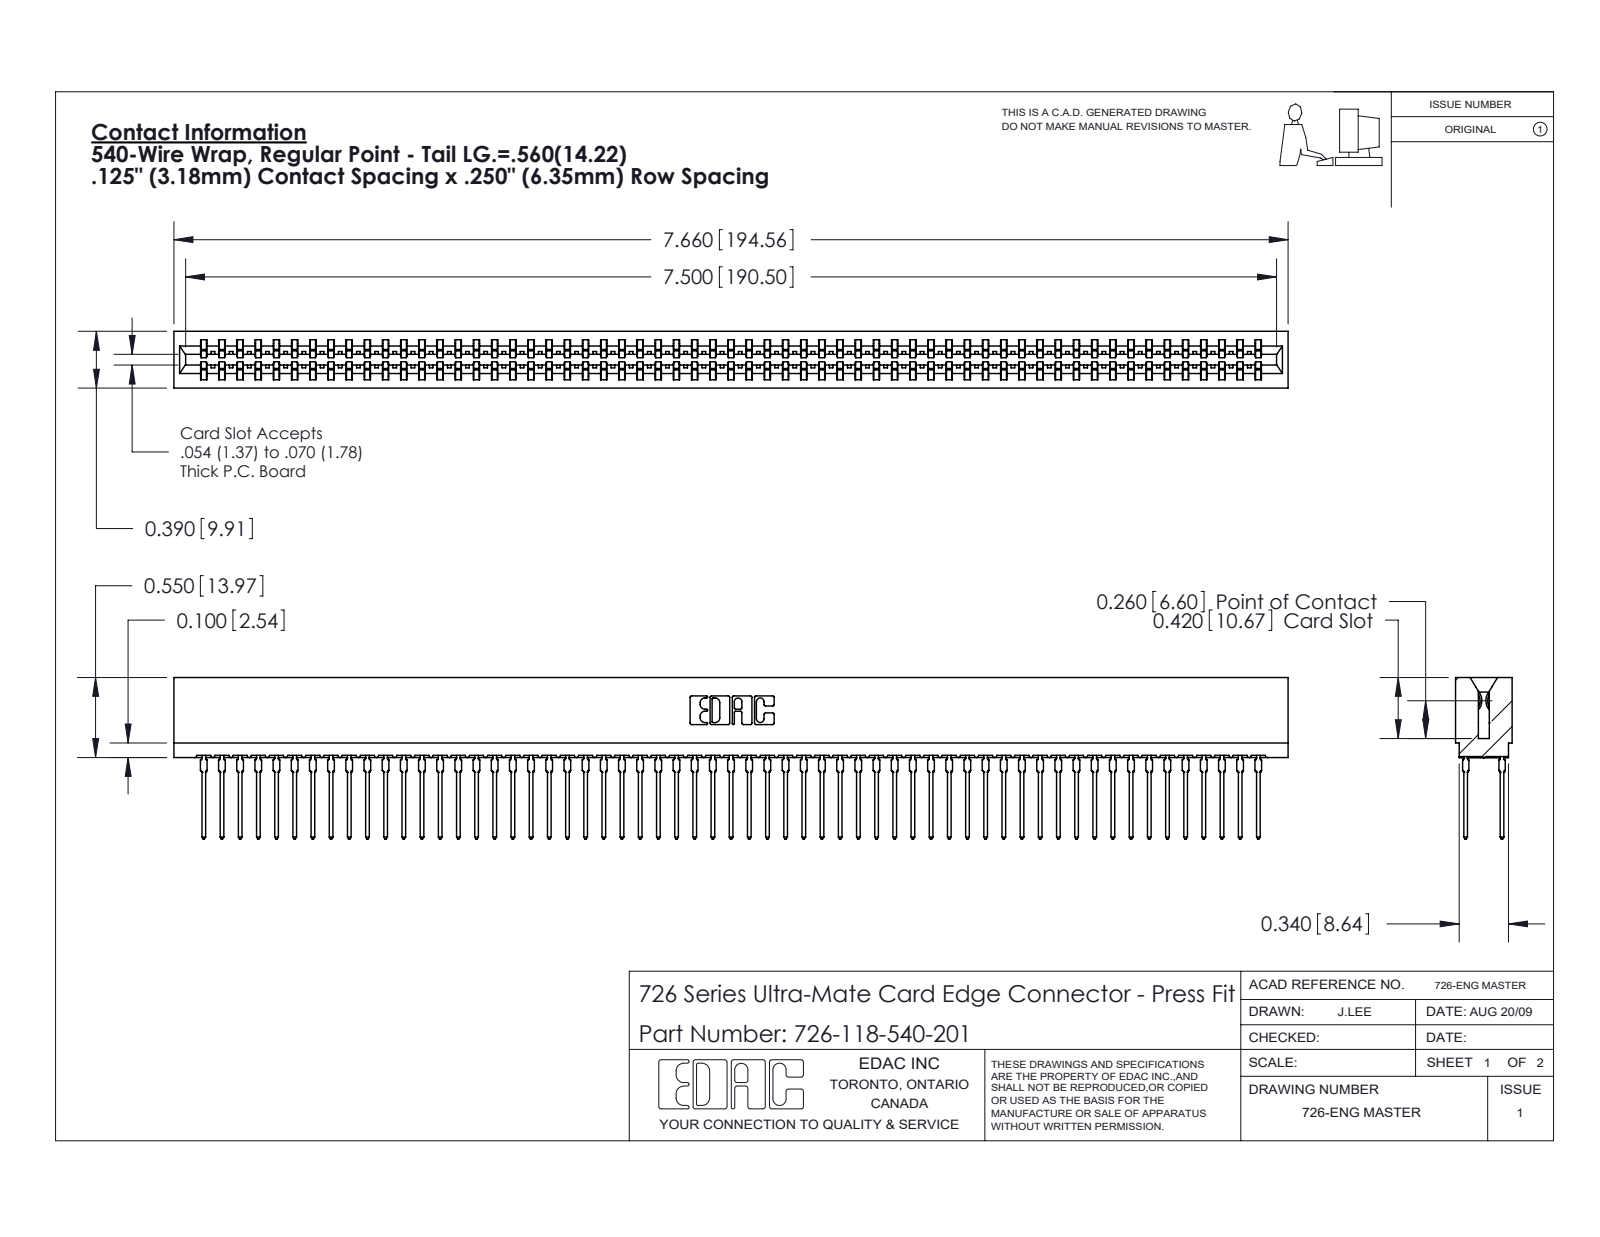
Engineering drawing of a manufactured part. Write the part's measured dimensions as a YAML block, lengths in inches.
part_name: "746-292-001_540; 726-118-540-201; 726 Part_.515 Slot Depth - 01"
step_written_by: "SolidWorks 2020 (CONFIG_CONTROL_DESIGN)"
units: inches
bodies: {solids: 119, faces: 10658, planar: 5483, cylindrical: 2107, other: 3068}
overall_size: [7.66, 1.109, 0.39]
volume: 1.11
surface_area: 49.98
partial_cylinders:
  - {radius: 0.021, count: 236}
  - {radius: 0.015, count: 60}
  - {radius: 0.01, count: 22}
  - {radius: 0.005, count: 8}
  - {radius: 0.011, count: 8}
  - {radius: 0.007, count: 6}
  - {radius: 0.031, count: 6}
  - {radius: 0.026, count: 3}
face_to_face_distances: [0.057, 0.333, 0.025, 0.307, 0.25, 0.39, 0.275, 0.083, 0.365, 0.032]
